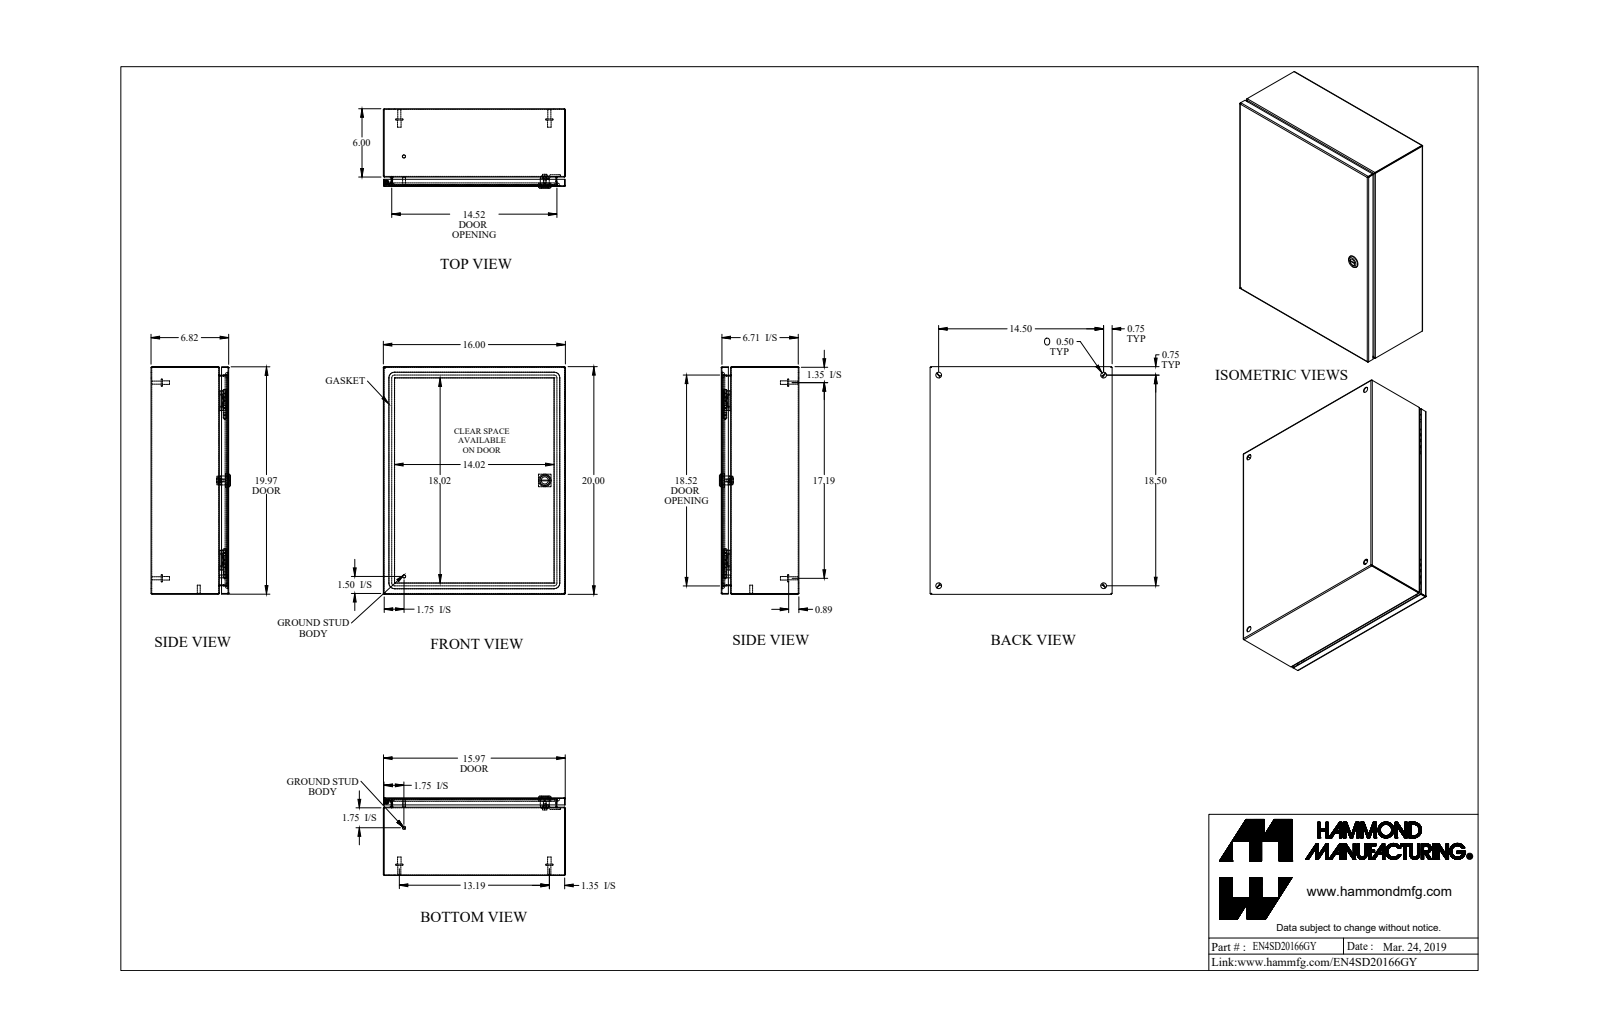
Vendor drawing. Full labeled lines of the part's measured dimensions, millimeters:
Part name (STEP PRODUCT): EN4SD20166GY_Default
STEP written by: SolidWorks 2019 (CONFIG_CONTROL_DESIGN)
Units: millimetres
Bodies: 21 solids, 634 faces (285 planar, 213 cylindrical, 136 other)
Overall size (bounding box): 508 × 406.4 × 177.3
Volume: 1 250 000 mm³ · Surface area: 1 668 000 mm²
Round holes (diameter × count): ⌀12.7 ×4, ⌀4.4 ×1, ⌀5.9 ×1, ⌀6.1 ×1, ⌀6.1 ×1, ⌀15.9 ×1, ⌀19.9 ×1
Round bosses / shafts (diameter × count): ⌀15.9 ×4, ⌀8 ×4, ⌀6.9 ×4, ⌀7.1 ×2, ⌀6.4 ×2, ⌀27.9 ×1, ⌀13.3 ×1, ⌀11.6 ×1
Partial cylindrical surfaces — rounded edges, fillets, slot ends (radius × count): R0.7 ×21, R2.2 ×21, R6.4 ×16, R482.6 ×8, R0.2 ×4, R1.6 ×4, R12.7 ×4, R3.2 ×2
Main face-to-face distances: 1.4, 171.8, 170.4, 173.3, 405, 506.6, 403.5, 406.4, 505.1, 508
Hole centre spacings: 368.3, 469.9, 597.1, 236.5, 236.5, 414.4, 414.5
